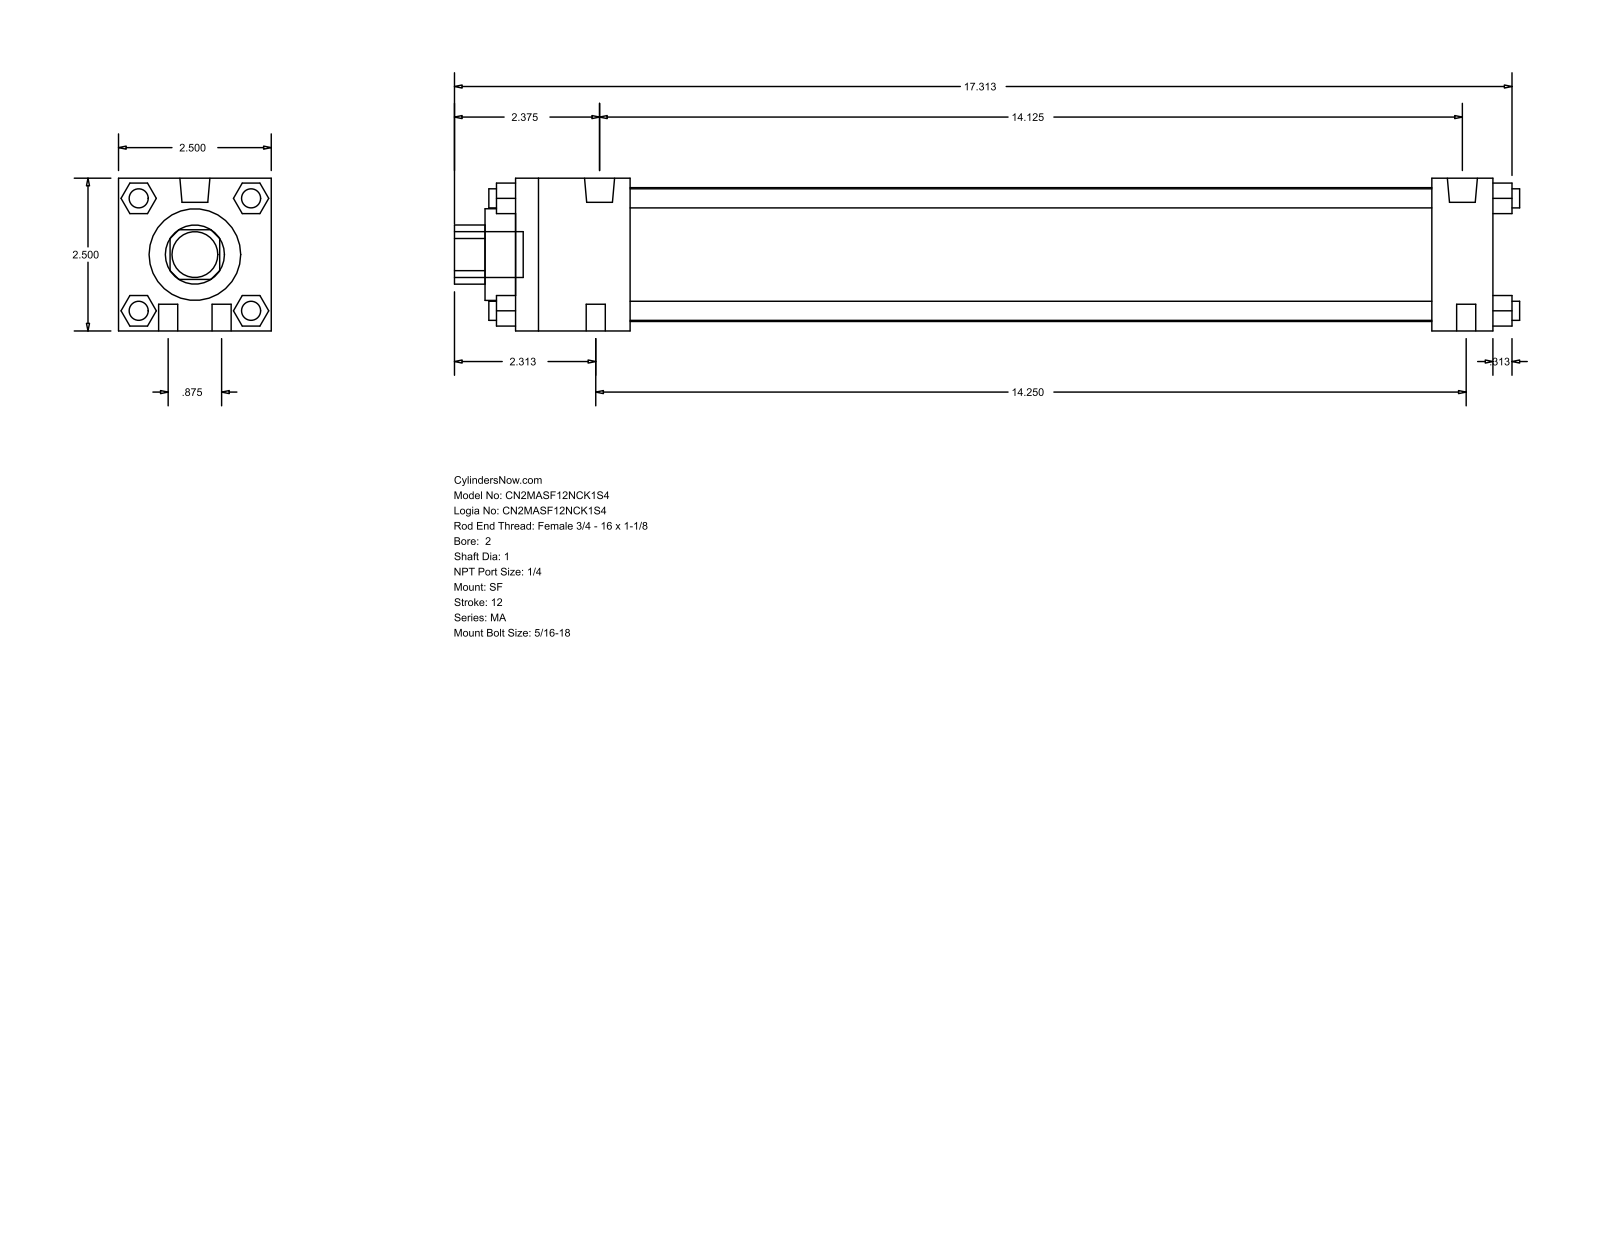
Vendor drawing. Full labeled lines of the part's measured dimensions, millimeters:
Part name (STEP PRODUCT): MA_SF__0200_1
STEP written by: GSSL Pune (CONFIG_CONTROL_DESIGN)
Units: millimetres
Bodies: 0 solids, 124 faces (94 planar, 30 cylindrical, 0 other)
Overall size (bounding box): 442.91 × 63.5 × 63.5
Round holes (diameter × count): ⌀25.4 ×1, ⌀38.1 ×1, ⌀55.63 ×1
Round bosses / shafts (diameter × count): ⌀7.94 ×10, ⌀12.49 ×2, ⌀19.05 ×1
Partial cylindrical surfaces — rounded edges, fillets, slot ends (radius × count): R12.29 ×1
Main face-to-face distances: 63.5, 406.4, 12.7, 25.4, 381, 47.63, 333.37, 358.77, 23.37, 40.47
